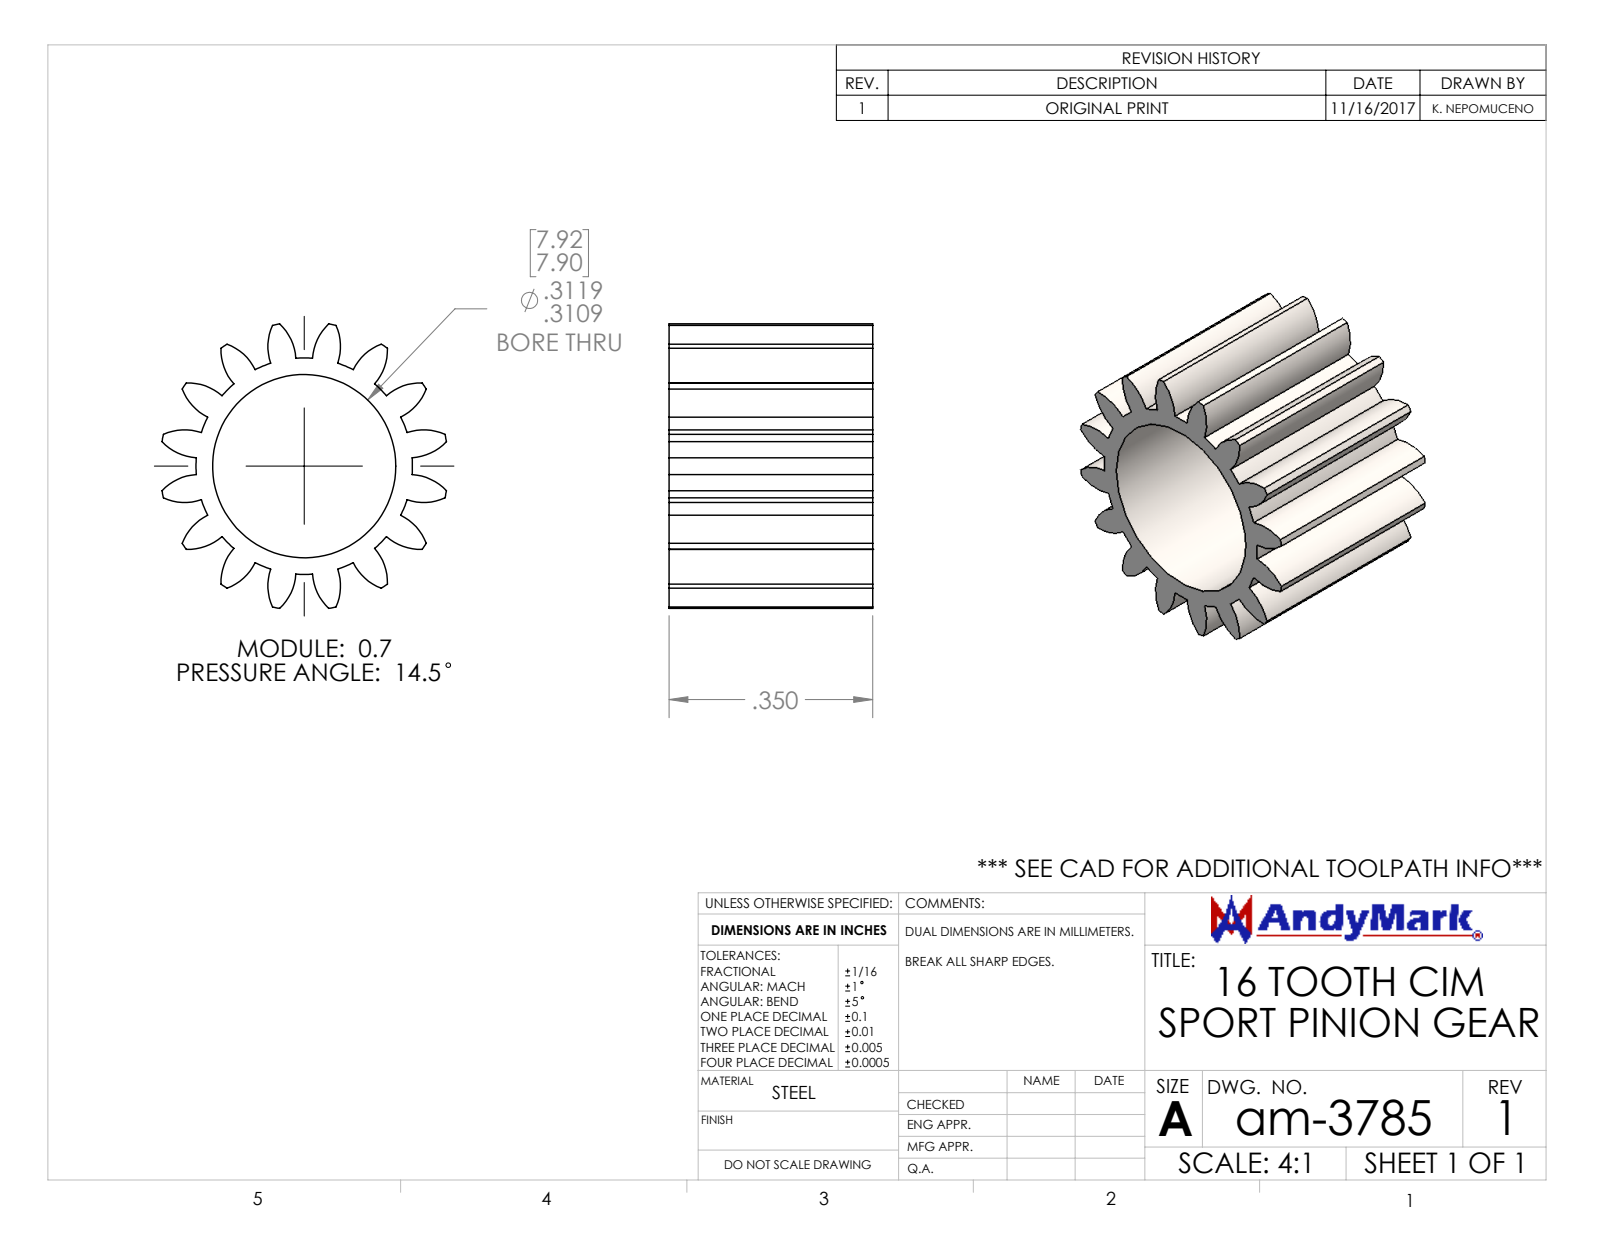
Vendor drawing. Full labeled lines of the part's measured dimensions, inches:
Part name (STEP PRODUCT): am-3785 - CIM Sport 16T Pinion Gear
STEP written by: SolidWorks 2017 (CONFIG_CONTROL_DESIGN)
Units: inches
Bodies: 1 solid, 73 faces (2 planar, 71 cylindrical, 0 other)
Overall size (bounding box): 0.489 × 0.489 × 0.35
Volume: 0.024 in³ · Surface area: 1.462 in²
Round holes (diameter × count): ⌀0.315 ×1
Partial cylindrical surfaces — rounded edges, fillets, slot ends (radius × count): R0.088 ×32, R0.186 ×1, R0.248 ×1
Main face-to-face distances: 0.35
